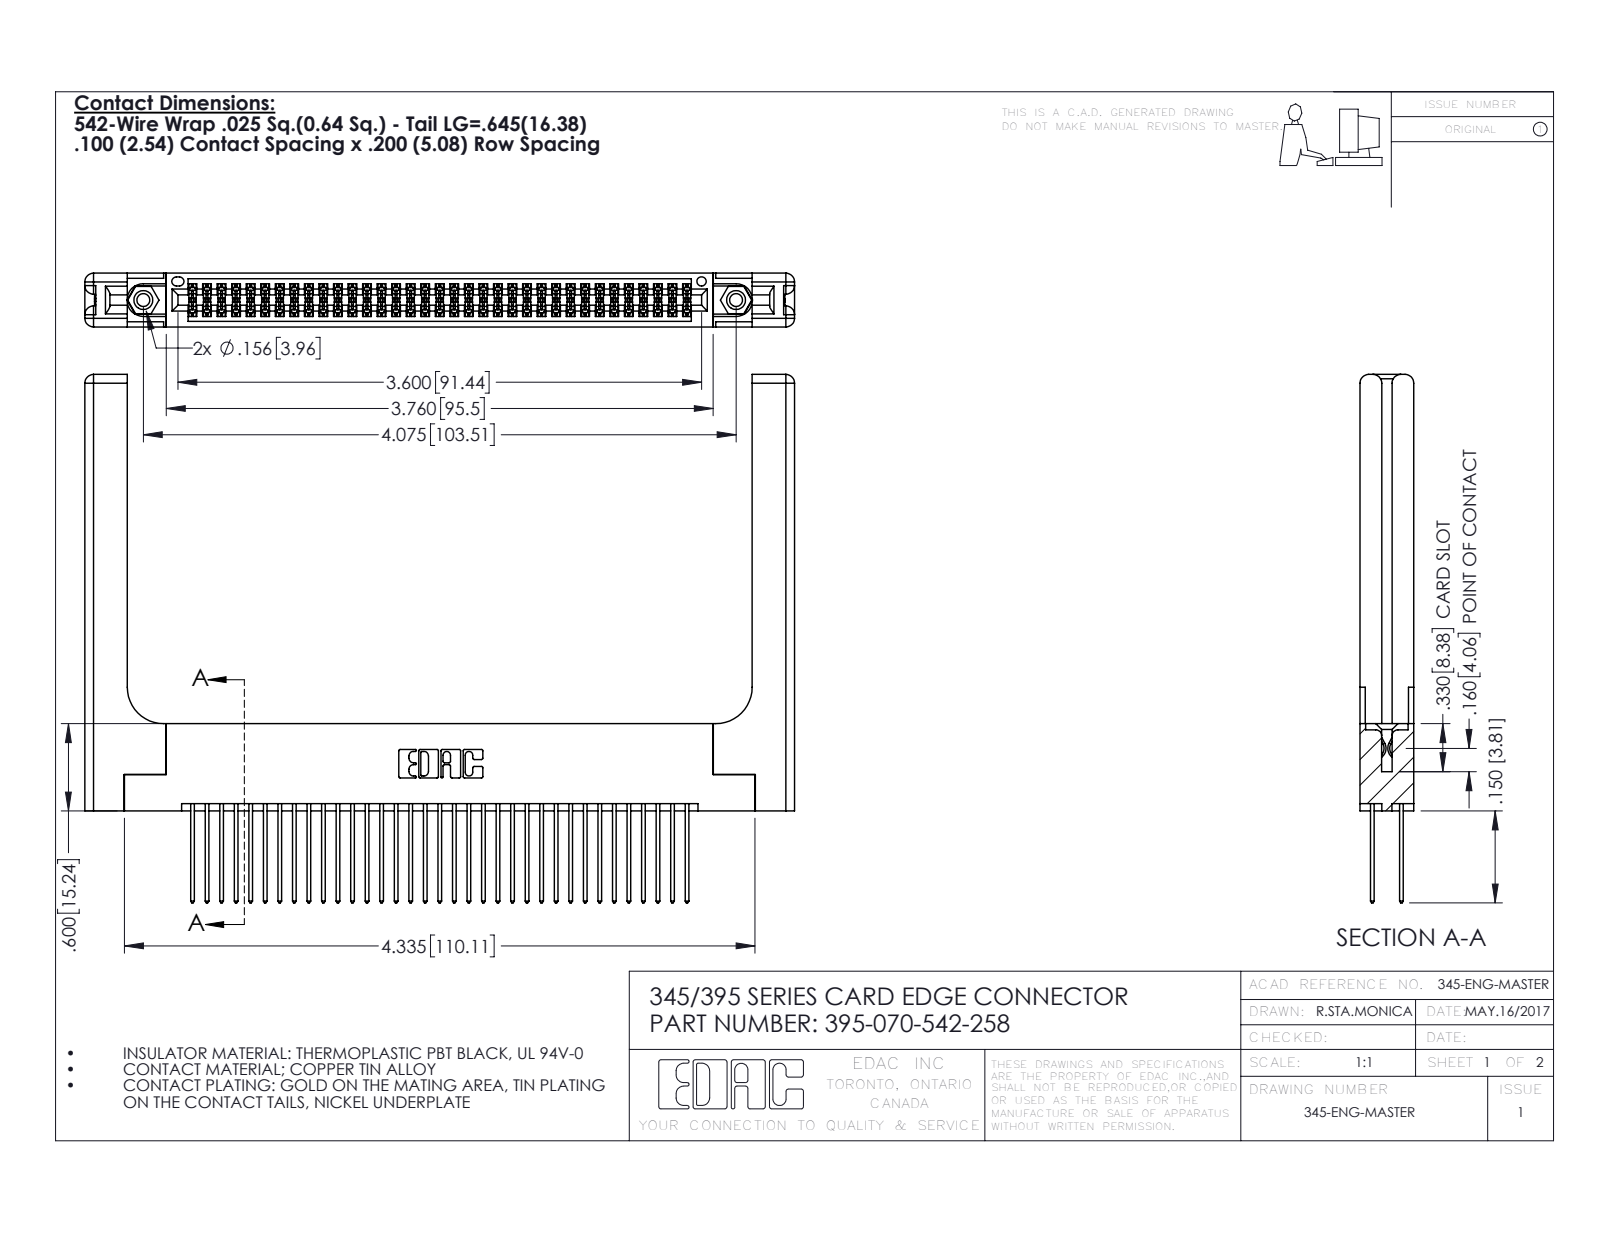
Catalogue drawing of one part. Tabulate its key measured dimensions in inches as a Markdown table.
| quantity | value |
| --- | --- |
| part name | 395-070-542-258; 345-220-058_345-220-058; 345-250-001_345-250-001-102; 345 Part_Flush Mounting Lugs - 0.156 Dia-TH (+1 more) |
| STEP written by | SolidWorks 2016 (CONFIG_CONTROL_DESIGN) |
| units | inches |
| bodies | 75 solids, 3882 faces (2538 planar, 1284 cylindrical, 60 other) |
| overall size | 4.879 × 3.632 × 0.37 |
| volume | 1.268 in³ |
| surface area | 38.18 in² |
| round holes (diameter × count) | 0.089 × 2, 0.125 × 2, 0.156 × 2, 0.064 × 1 |
| round bosses / shafts (diameter × count) | 0.155 × 2 |
| partial cylindrical surfaces (radius × count) | 0.006 × 105, 0.01 × 70, 0.01 × 22, 0.06 × 16, 0.007 × 6, 0.031 × 6, 0.026 × 3, 0.014 × 2 |
| main face-to-face distances | 0.072, 0.298, 0.37, 0.2, 0.098, 0.272, 0.025, 0.225, 0.175, 0.148 |
| hole center spacings | 0.27, 3.839, 4.075 |
